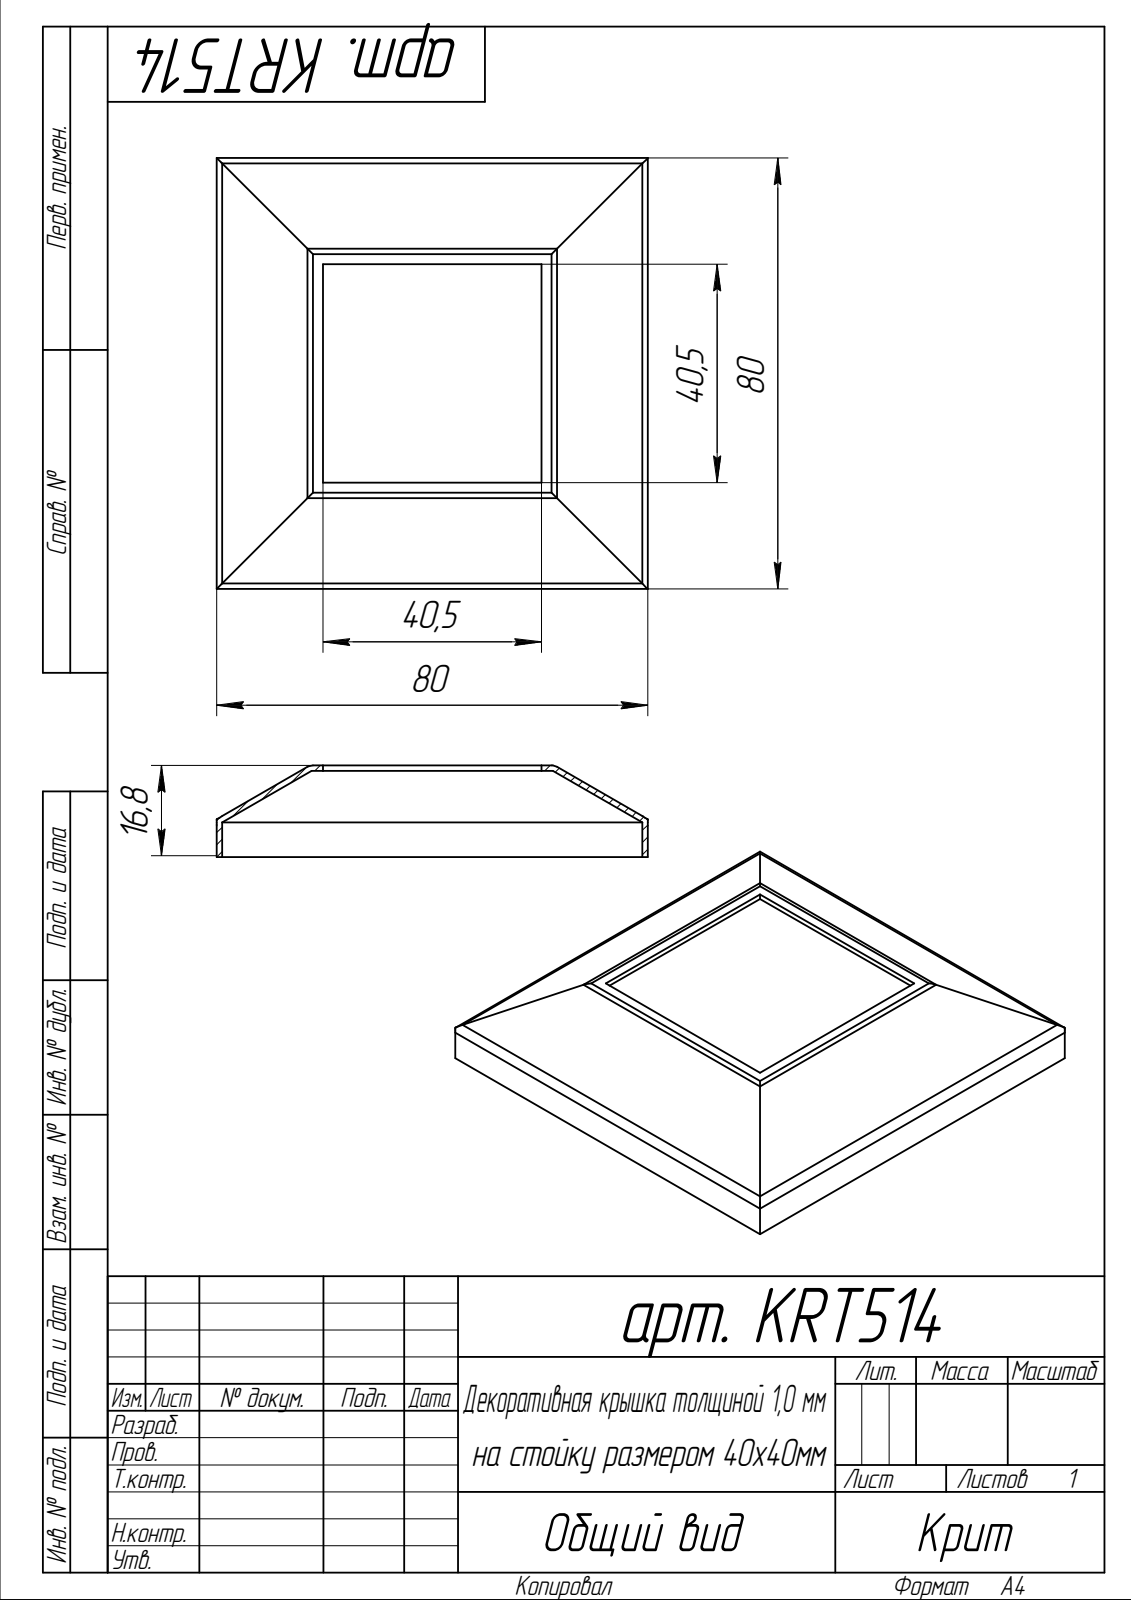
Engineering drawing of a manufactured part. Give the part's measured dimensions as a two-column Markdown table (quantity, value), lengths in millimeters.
| quantity | value |
| --- | --- |
| part name | арт. KRT514 |
| STEP written by | SolidWorks 2014 (AUTOMOTIVE_DESIGN) |
| units | millimeters |
| bodies | 1 solid, 31 faces (23 planar, 4 cylindrical, 4 other) |
| overall size | 80 × 80 × 17 |
| volume | 7 033 mm³ |
| surface area | 15 179 mm² |
| partial cylindrical surfaces (radius × count) | 2 × 4 |
| main face-to-face distances | 1, 79, 78, 80, 16, 17, 19.75, 60.25, 18.75, 59.25 |
